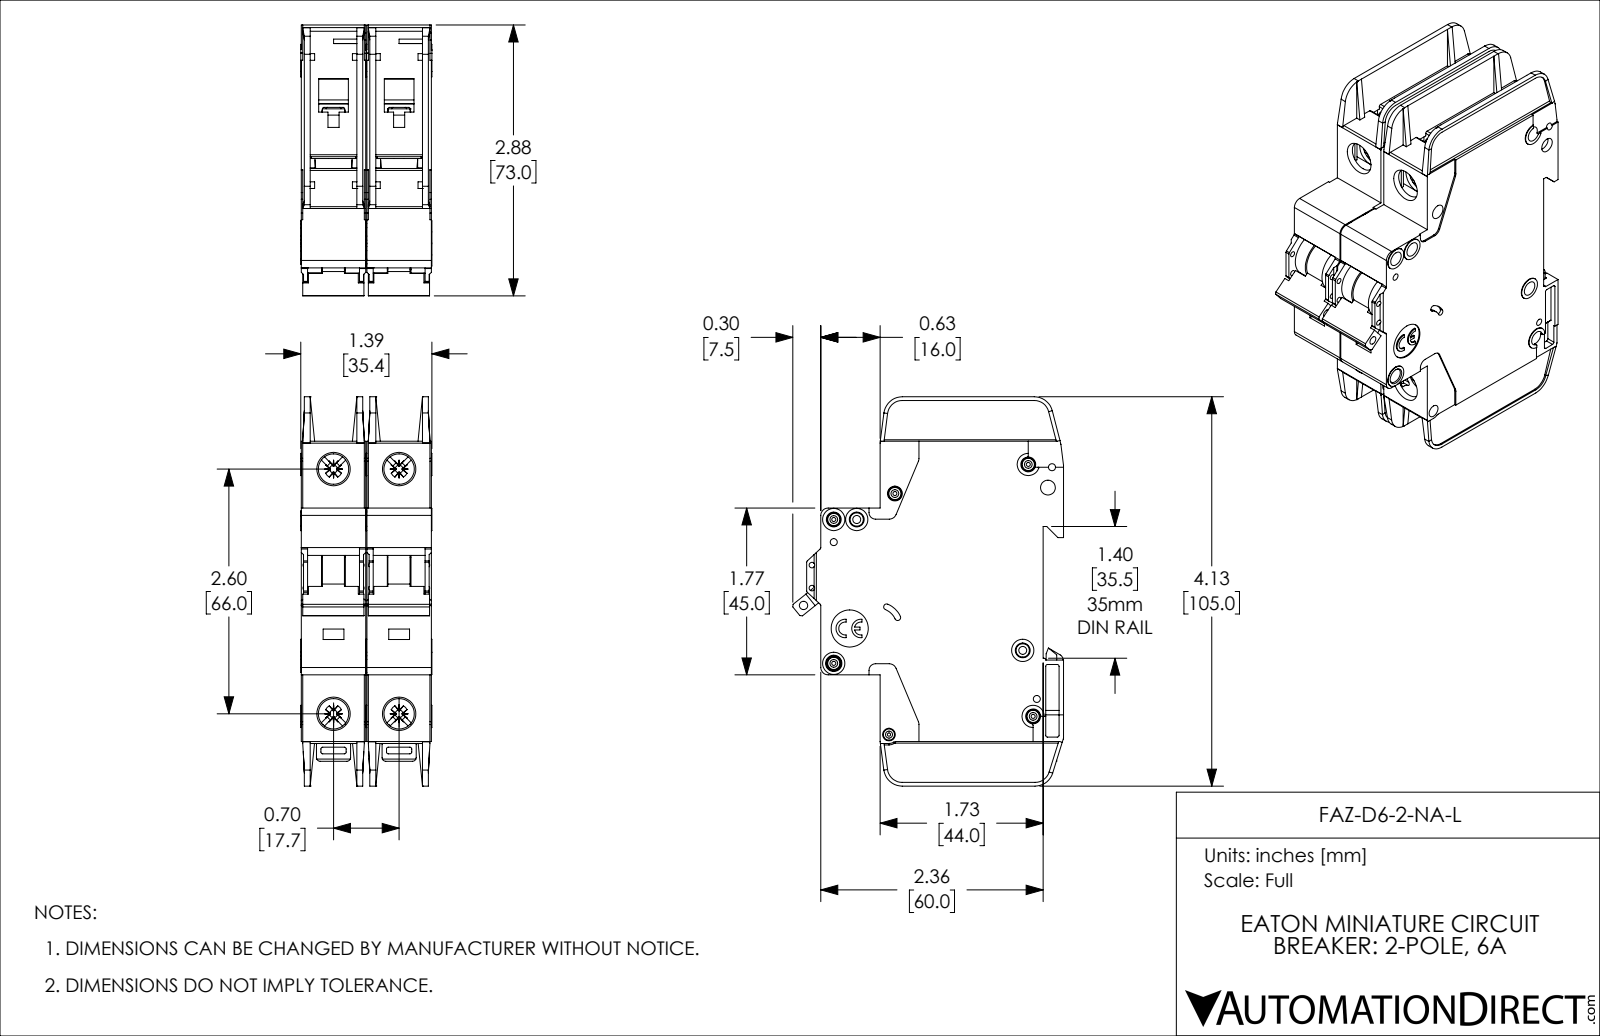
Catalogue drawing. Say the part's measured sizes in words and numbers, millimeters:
The part is named "FAZ-D6-2-NA-L". Its 3-D file was written by "SolidWorks 2019 (AUTOMOTIVE_DESIGN)". It is 2 solids with 2254 faces: 1342 planar, 714 cylindrical and 198 other. Overall it measures 105 by 73.1 by 35.4 millimeters. Its volume is 153 500 cubic millimeters and its surface area 52 910 square millimeters. Round holes: 8 of diameter 4, 5 of diameter 1.1, 4 of diameter 1.9, 4 of diameter 8.2, 2 of diameter 1.5, 2 of diameter 2.2, 1 of diameter 0.9, 1 of diameter 2.3, 1 of diameter 2.5, 1 of diameter 3.4, 1 of diameter 10. Round bosses or shafts: 5 of diameter 3.3, 4 of diameter 6, 3 of diameter 3, 2 of diameter 2.5. Partial cylindrical surfaces (rounded edges, fillets, slot ends): 57 of radius 0.5, 20 of radius 0.4, 14 of radius 1, 10 of radius 2, 8 of radius 1.1, 5 of radius 0.2, 5 of radius 5, 4 of radius 0.3. The main face-to-face distances are 17.7, 1.2, 17.4, 15, 2.4, 16.2, 13.8, 35.1, 18.9, 16.5. The hole center spacings are 6.2, 13.6, 17.7, 22.1, 66, 68.3, 4.8, 5.1.
